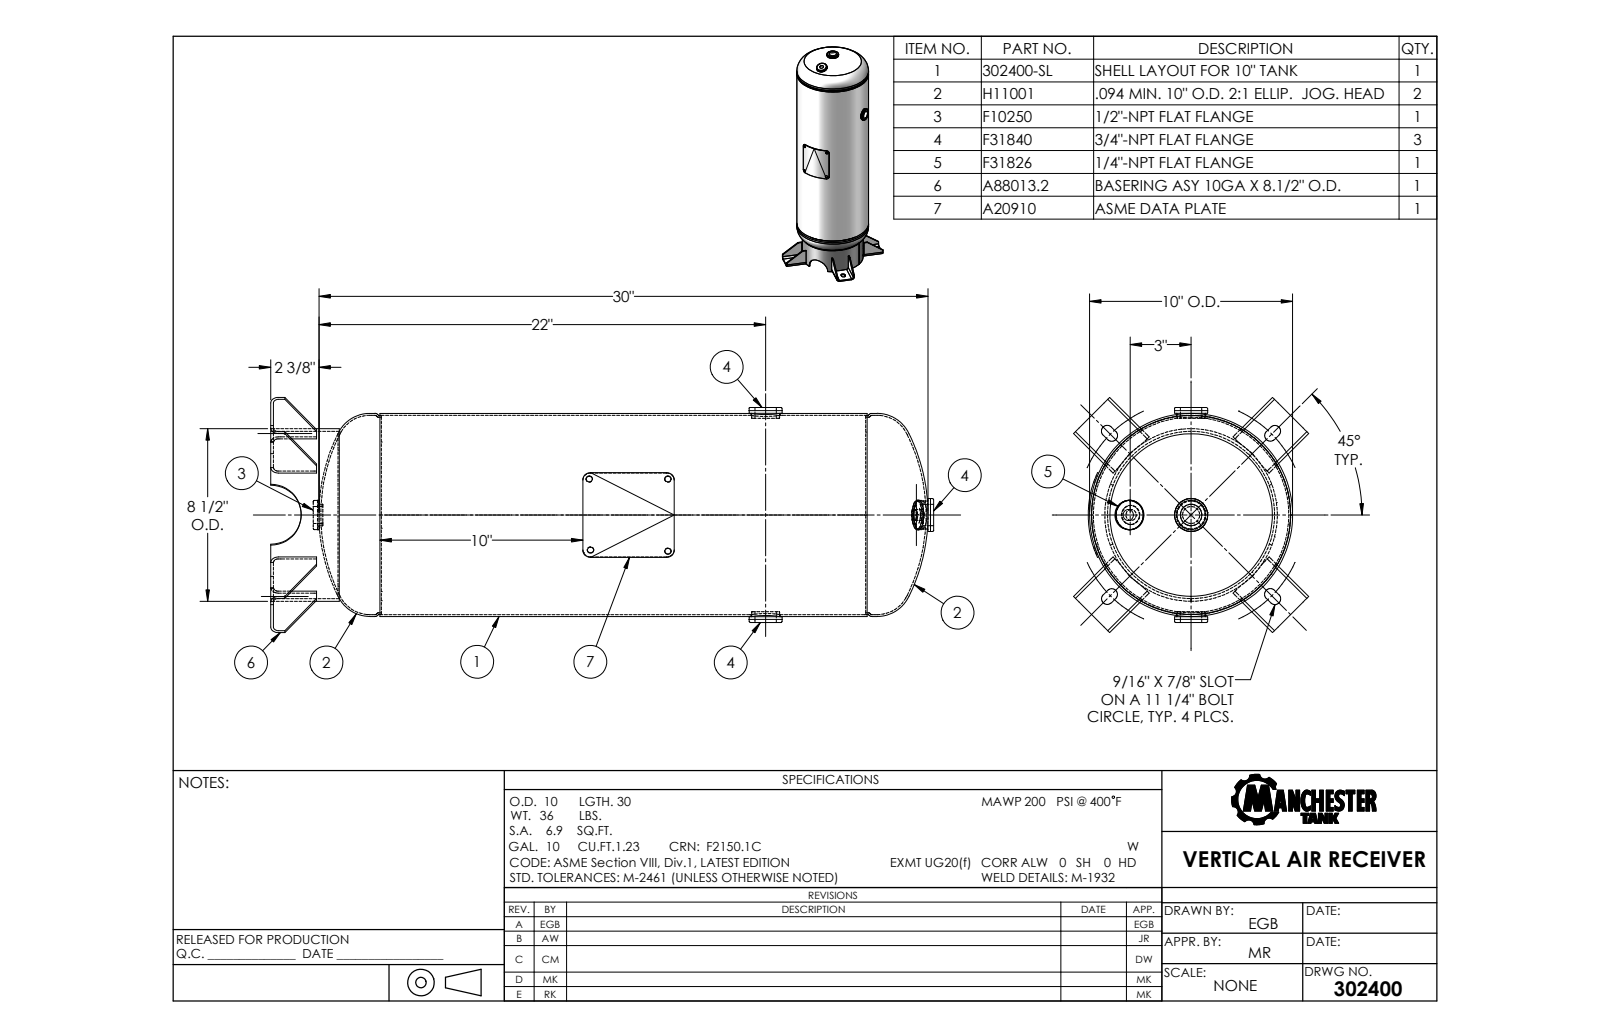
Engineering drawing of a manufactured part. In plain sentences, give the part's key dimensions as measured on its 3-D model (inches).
The part is named "302400". Its 3-D file was written by "SolidWorks 2011 (CONFIG_CONTROL_DESIGN)". It is 0 solids with 239 faces: 100 planar, 79 cylindrical and 60 other. Overall it measures 32.659 by 11.671 by 11.671 inches. Round holes: 2 of diameter 1.05, 1 of diameter 0.54, 1 of diameter 0.84, 1 of diameter 8.232, 1 of diameter 9.624, 1 of diameter 9.812. Round bosses or shafts: 2 of diameter 1.63, 2 of diameter 1.45, 2 of diameter 1.438, 1 of diameter 10, 1 of diameter 9.79, 1 of diameter 8.5, 1 of diameter 1.625, 1 of diameter 1.625. Partial cylindrical surfaces (rounded edges, fillets, slot ends): 8 of radius 0.25, 8 of radius 0.281, 8 of radius 0.384, 1 of radius 5.06. The main face-to-face distances are 0.134, 0.063, 2.446, 0.134, 2.509, 2.58, 0.071, 0.197, 2.383, 2.313.
